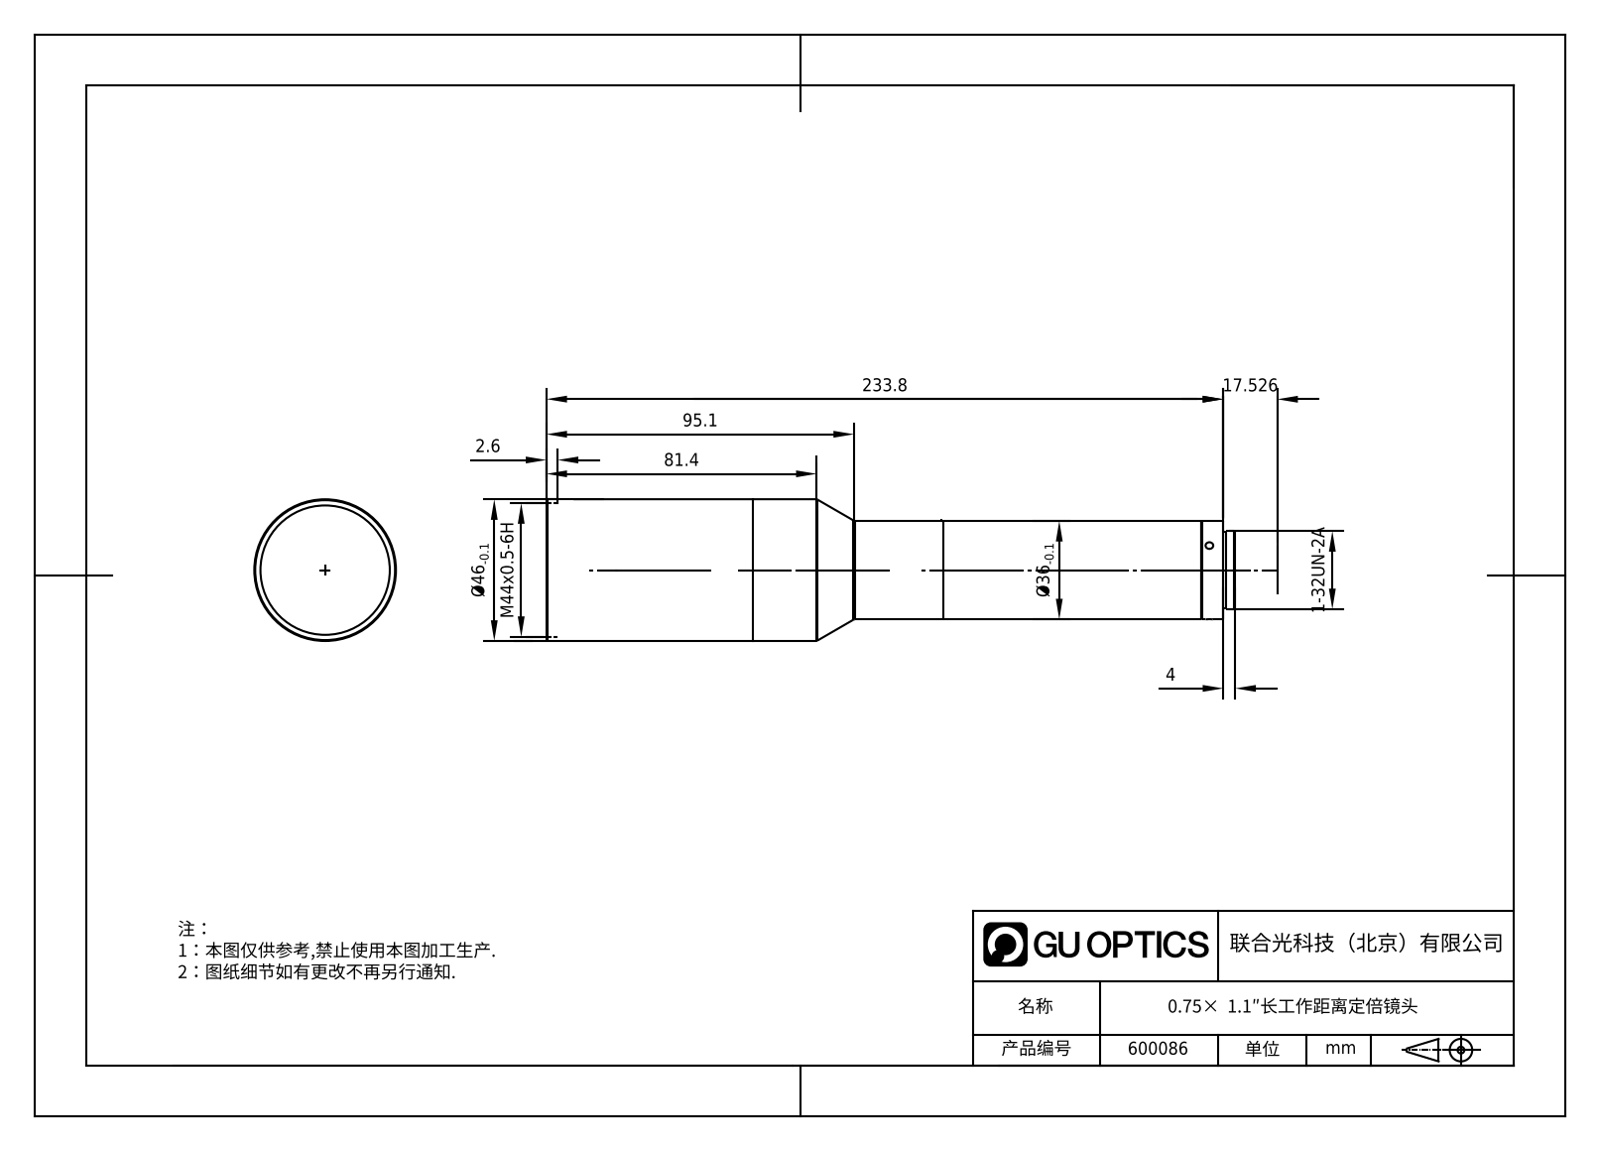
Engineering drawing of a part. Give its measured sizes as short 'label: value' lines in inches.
name: 600086
written by: SolidWorks 2020 (CONFIG_CONTROL_DESIGN)
unit: in
bodies: 2 solids, 28 faces (7 planar, 12 cylindrical, 9 other)
size: 9.361 × 1.811 × 1.811
volume: 17.73 in³; area: 56.86 in²
holes: 3× ⌀0.098, 1× ⌀1.654
bosses: 1× ⌀1.811, 1× ⌀1.417, 1× ⌀1, 1× ⌀0.969
rounds: 1× R0.672
face distances: 8.85, 0.157, 9.007, 9.361, 9.204, 0.354, 0.126, 0.031, 8.881, 9.235
